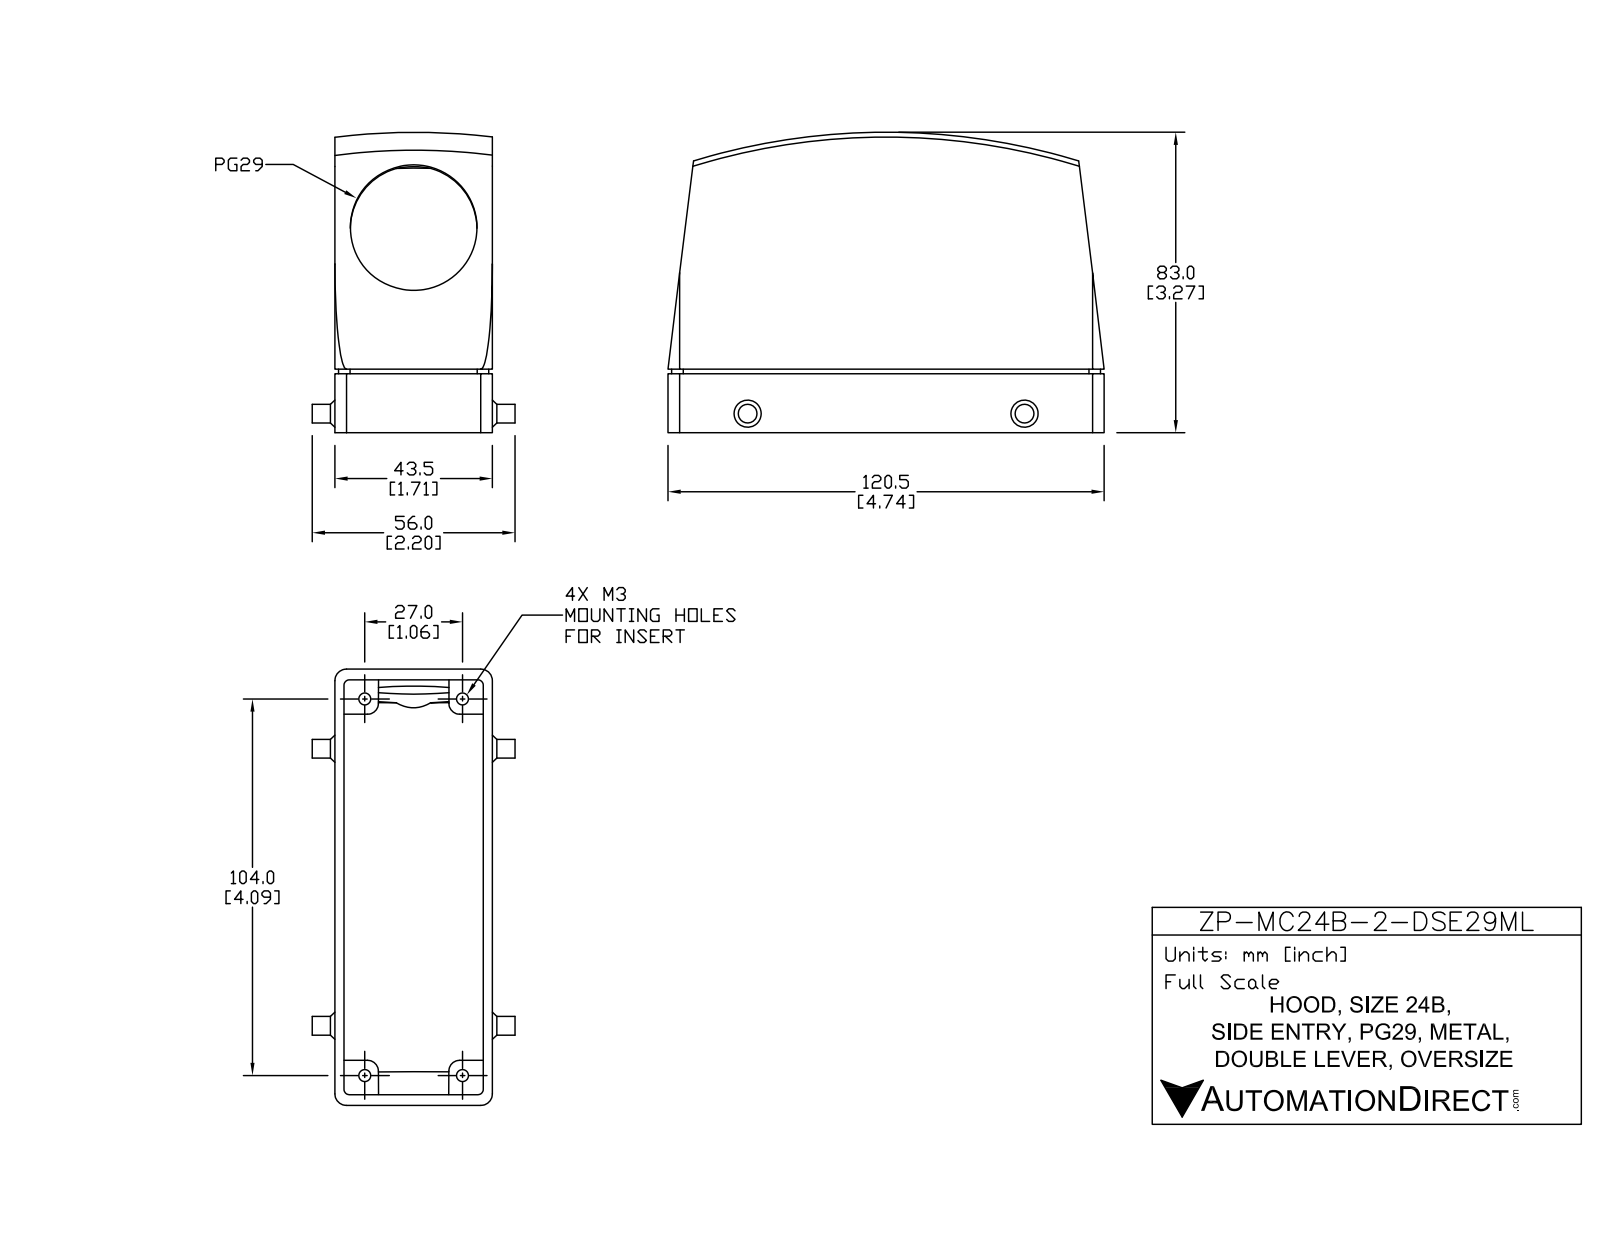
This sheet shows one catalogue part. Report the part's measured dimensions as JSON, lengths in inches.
{"part_name": "ZP-MC24B-2-DSE29ML", "step_written_by": "SolidWorks 2011 (AUTOMOTIVE_DESIGN)", "units": "inches", "bodies": {"solids": 9, "faces": 104, "planar": 60, "cylindrical": 34, "other": 10}, "overall_size": [4.744, 3.053, 2.205], "volume_in3": 4.704, "surface_area_in2": 94.07, "round_holes": [[0.13, 4], [1.378, 1]], "round_bosses_or_shafts": [[0.204, 2]], "partial_cylinders_radius": [[0.126, 8], [0.059, 4], [0.118, 4], [0.028, 1]], "face_to_face_distances": [0.098, 1.614, 1.713, 1.516, 0.374, 4.137, 0.117, 0.491, 4.254, 4.628], "hole_center_spacings": [1.063, 4.094, 4.23]}
